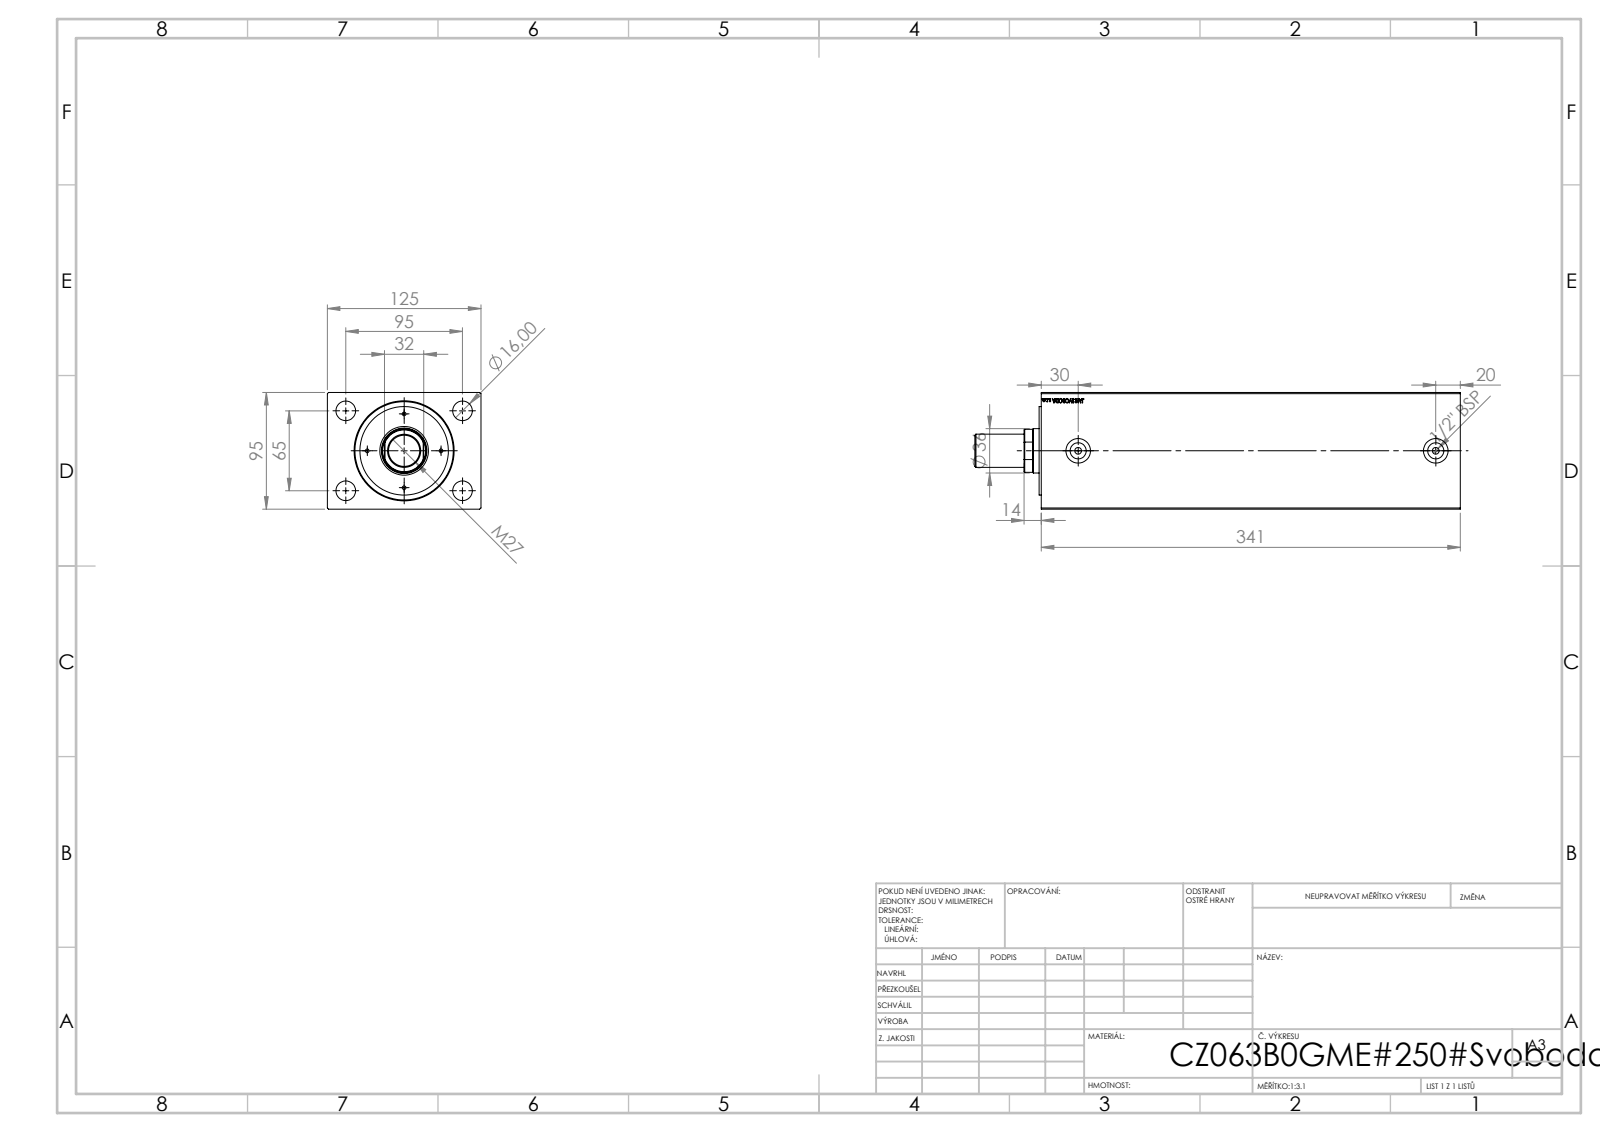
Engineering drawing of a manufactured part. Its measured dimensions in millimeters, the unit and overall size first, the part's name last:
Units: millimetres
Overall size (bounding box): 395 × 125 × 95
Round holes (diameter × count): ⌀3 ×4, ⌀16 ×4, ⌀5.5 ×2, ⌀13.16 ×2, ⌀20 ×2, ⌀25.5 ×1, ⌀36 ×1, ⌀37 ×1, ⌀63 ×1, ⌀80 ×1
Round bosses / shafts (diameter × count): ⌀72 ×1, ⌀27 ×1
Partial cylindrical surfaces — rounded edges, fillets, slot ends (radius × count): R17.5 ×1
Main face-to-face distances: 95, 125, 341, 320.2, 20.8, 14, 12.2, 1.8, 308, 328.8
Hole centre spacings: 30, 36.91, 42.43, 47.57, 57.55, 78.5, 84.04, 60
Volume: 3 488 000 mm³ · Surface area: 318 343 mm²
Bodies: 4 solids, 880 faces (402 planar, 60 cylindrical, 418 other)
Part name (STEP PRODUCT): V500CZ_SMALL_MALE_METRIC; V500CZ_B_VC; V500CZ
STEP written by: SolidWorks 2019 (CONFIG_CONTROL_DESIGN)
